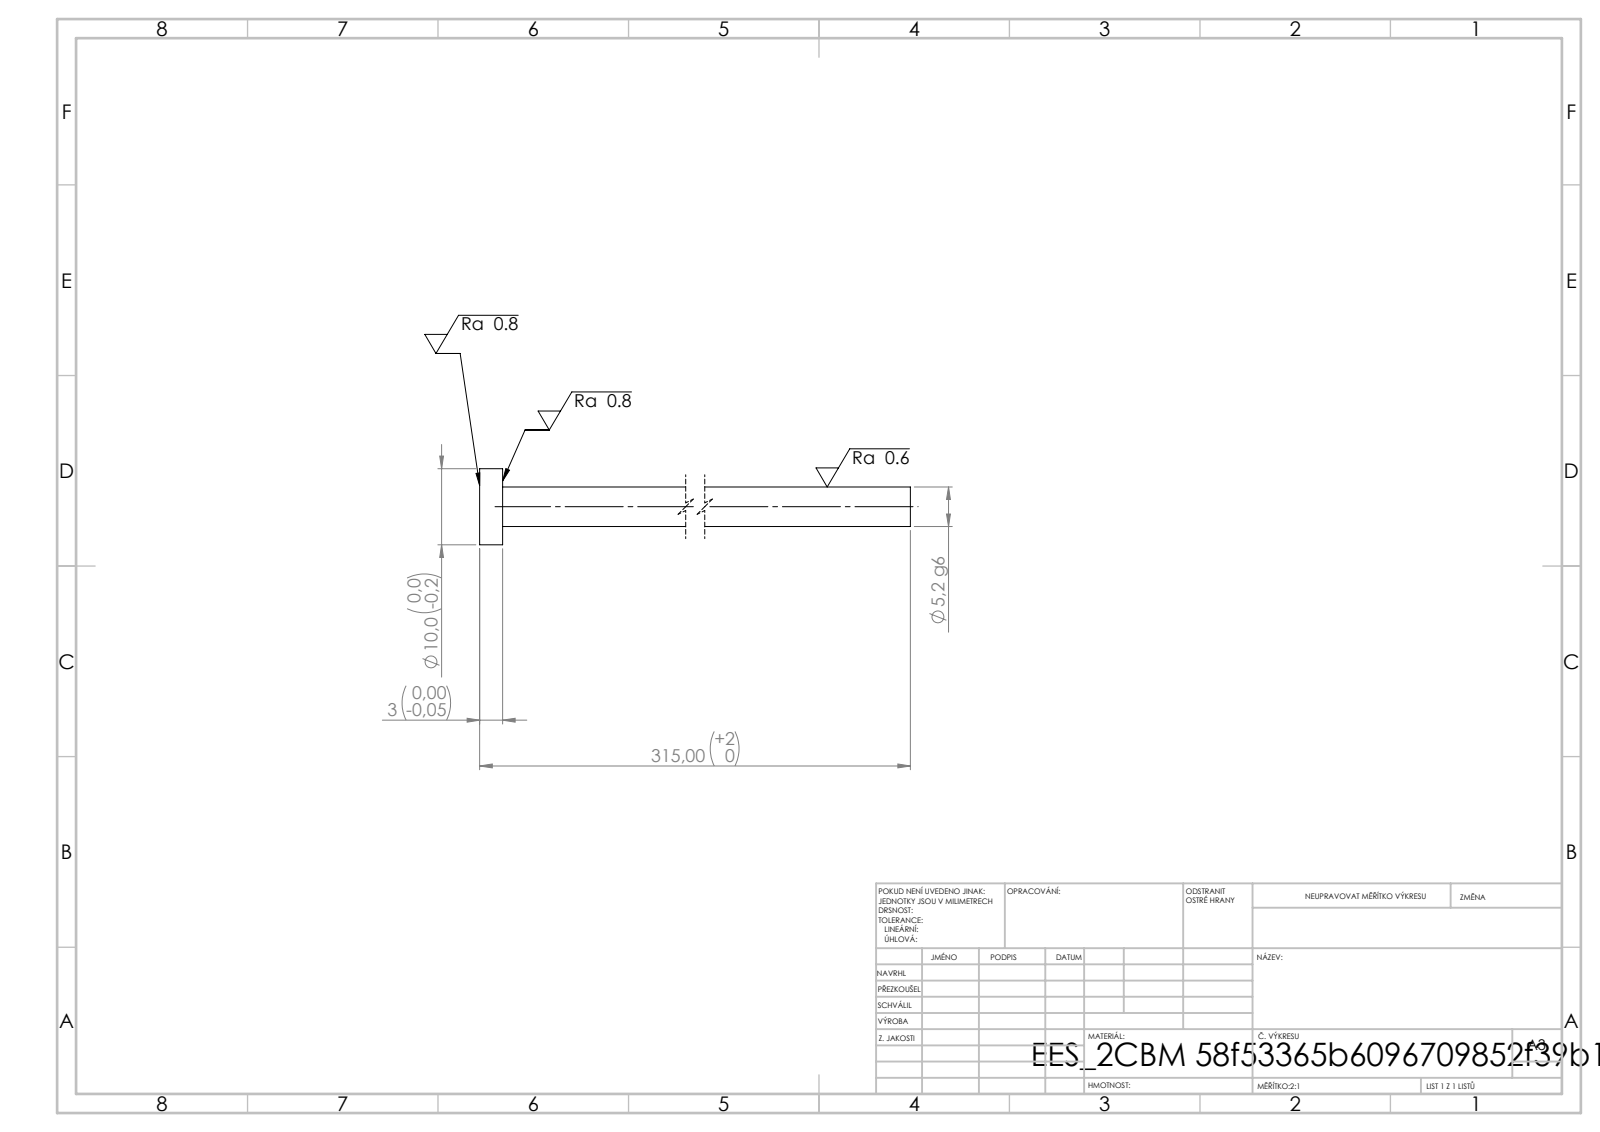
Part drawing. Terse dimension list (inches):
written by: SolidWorks 2019 (CONFIG_CONTROL_DESIGN)
unit: in
bodies: 1 solid, 7 faces (3 planar, 4 cylindrical, 0 other)
size: 12.402 × 0.394 × 0.394
volume: 0.419 in³; area: 8.289 in²
bosses: 1× ⌀0.394, 1× ⌀0.205
face distances: 0.118, 12.402, 12.283
